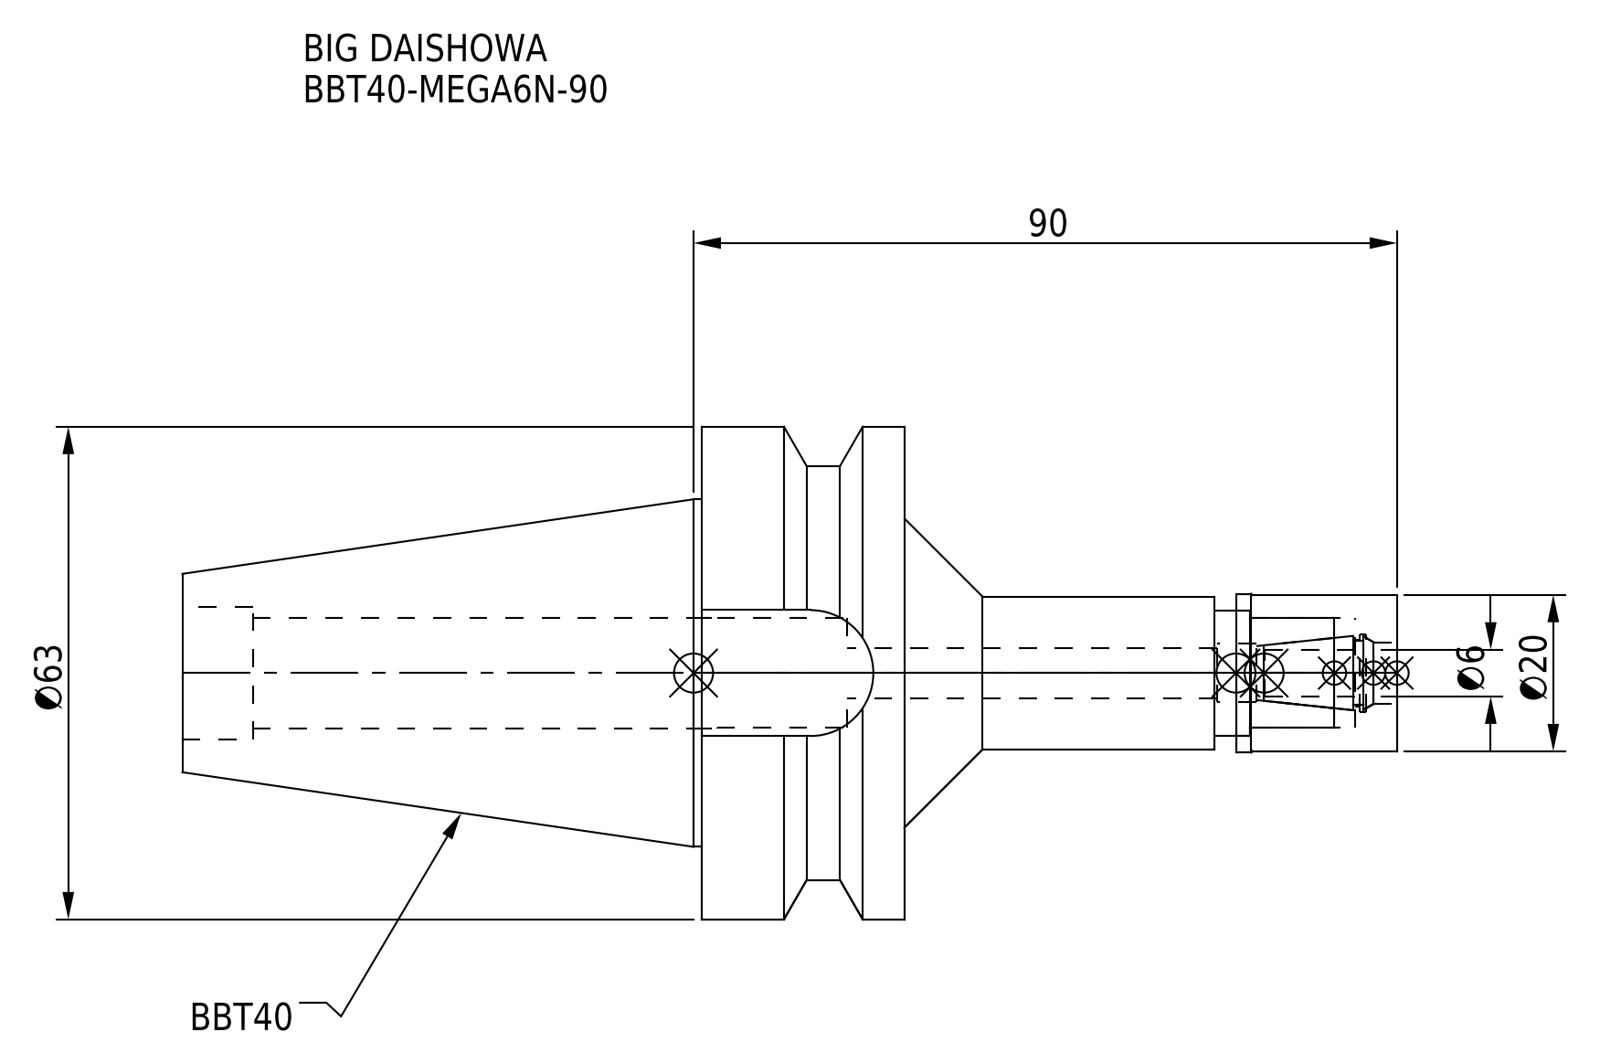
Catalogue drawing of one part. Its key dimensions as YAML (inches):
part_name: "MGN6_1.stp; DXF_TEMP_ASSY_ASM_4_ASM.stp; BBT40-MEGA6N-90-060.stp; BBT40-MEGA6N-90 (+3 more)"
step_written_by: "SolidWorks 2019 (CONFIG_CONTROL_DESIGN)"
units: inches
bodies: {solids: 2, faces: 80, planar: 24, cylindrical: 42, other: 14}
overall_size: [6.118, 2.48, 2.48]
volume: 8.642
surface_area: 45.75
round_holes:
  - {diameter: 0.252, count: 1}
  - {diameter: 0.295, count: 1}
  - {diameter: 0.311, count: 1}
  - {diameter: 0.335, count: 1}
  - {diameter: 0.394, count: 1}
  - {diameter: 0.551, count: 1}
  - {diameter: 0.555, count: 1}
  - {diameter: 0.559, count: 1}
  - {diameter: 0.63, count: 1}
  - {diameter: 0.669, count: 1}
round_bosses_or_shafts:
  - {diameter: 2.48, count: 1}
  - {diameter: 2.087, count: 1}
  - {diameter: 1.75, count: 1}
  - {diameter: 0.799, count: 1}
  - {diameter: 0.787, count: 1}
  - {diameter: 0.768, count: 1}
partial_cylinders:
  - {radius: 0.317, count: 1}
face_to_face_distances: [1.024, 1.772, 2.614, 3.638, 2.48, 3.504, 6.118, 0.634, 0.732, 3.346]
